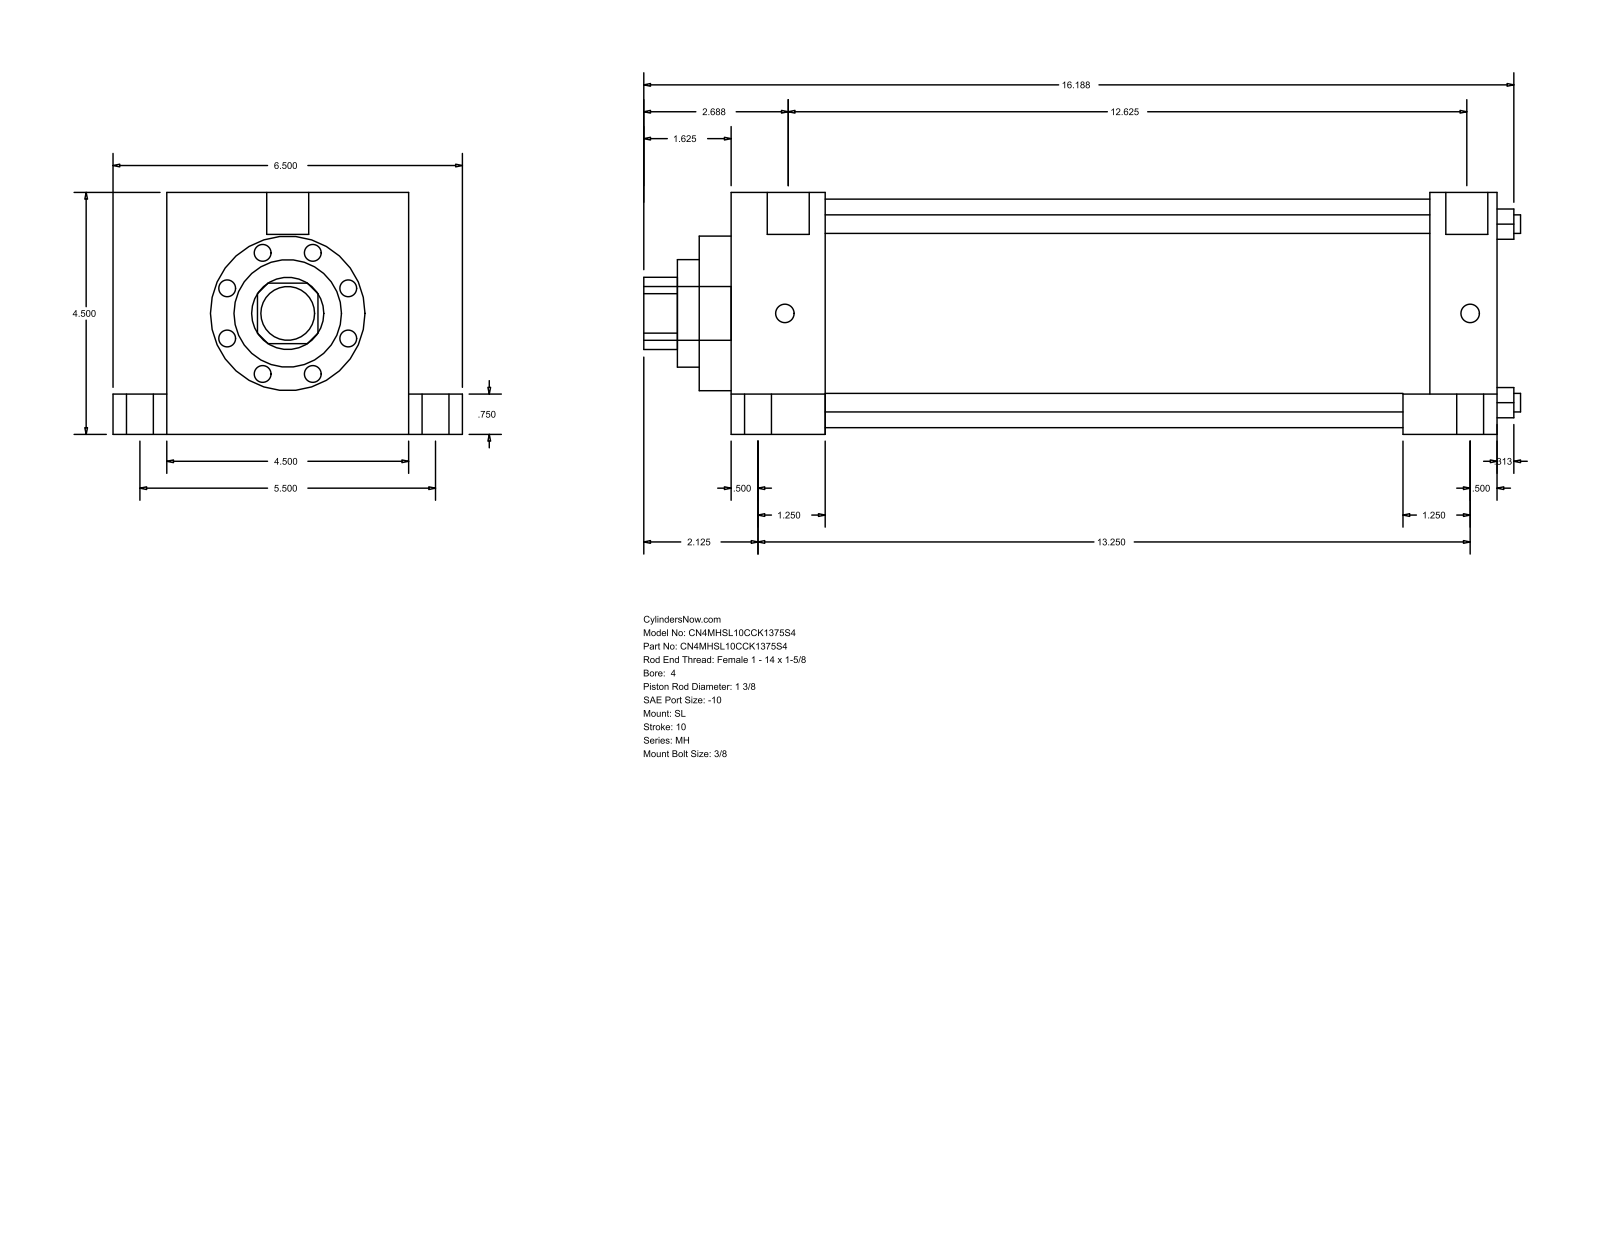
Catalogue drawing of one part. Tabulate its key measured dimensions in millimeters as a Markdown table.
| quantity | value |
| --- | --- |
| part name | MH_SL__0400_1.375 |
| STEP written by | GSSL Pune (CONFIG_CONTROL_DESIGN) |
| units | millimeters |
| bodies | 0 solids, 110 faces (77 planar, 33 cylindrical, 0 other) |
| overall size | 414.34 × 165.1 × 114.3 |
| round holes (diameter × count) | 8.76 × 4, 34.92 × 1, 50.8 × 1, 73.03 × 1, 107.95 × 1 |
| round bosses / shafts (diameter × count) | 19.05 × 4, 12.7 × 4, 8.73 × 4, 19.84 × 2, 25.4 × 1 |
| partial cylindrical surfaces (radius × count) | 17.06 × 1 |
| main face-to-face distances | 114.3, 361.96, 44.45, 317.51, 330.21, 285.76, 31.75, 25.4, 139.7, 19.05 |
| hole center spacings | 59.62, 84.32, 119.25 |
